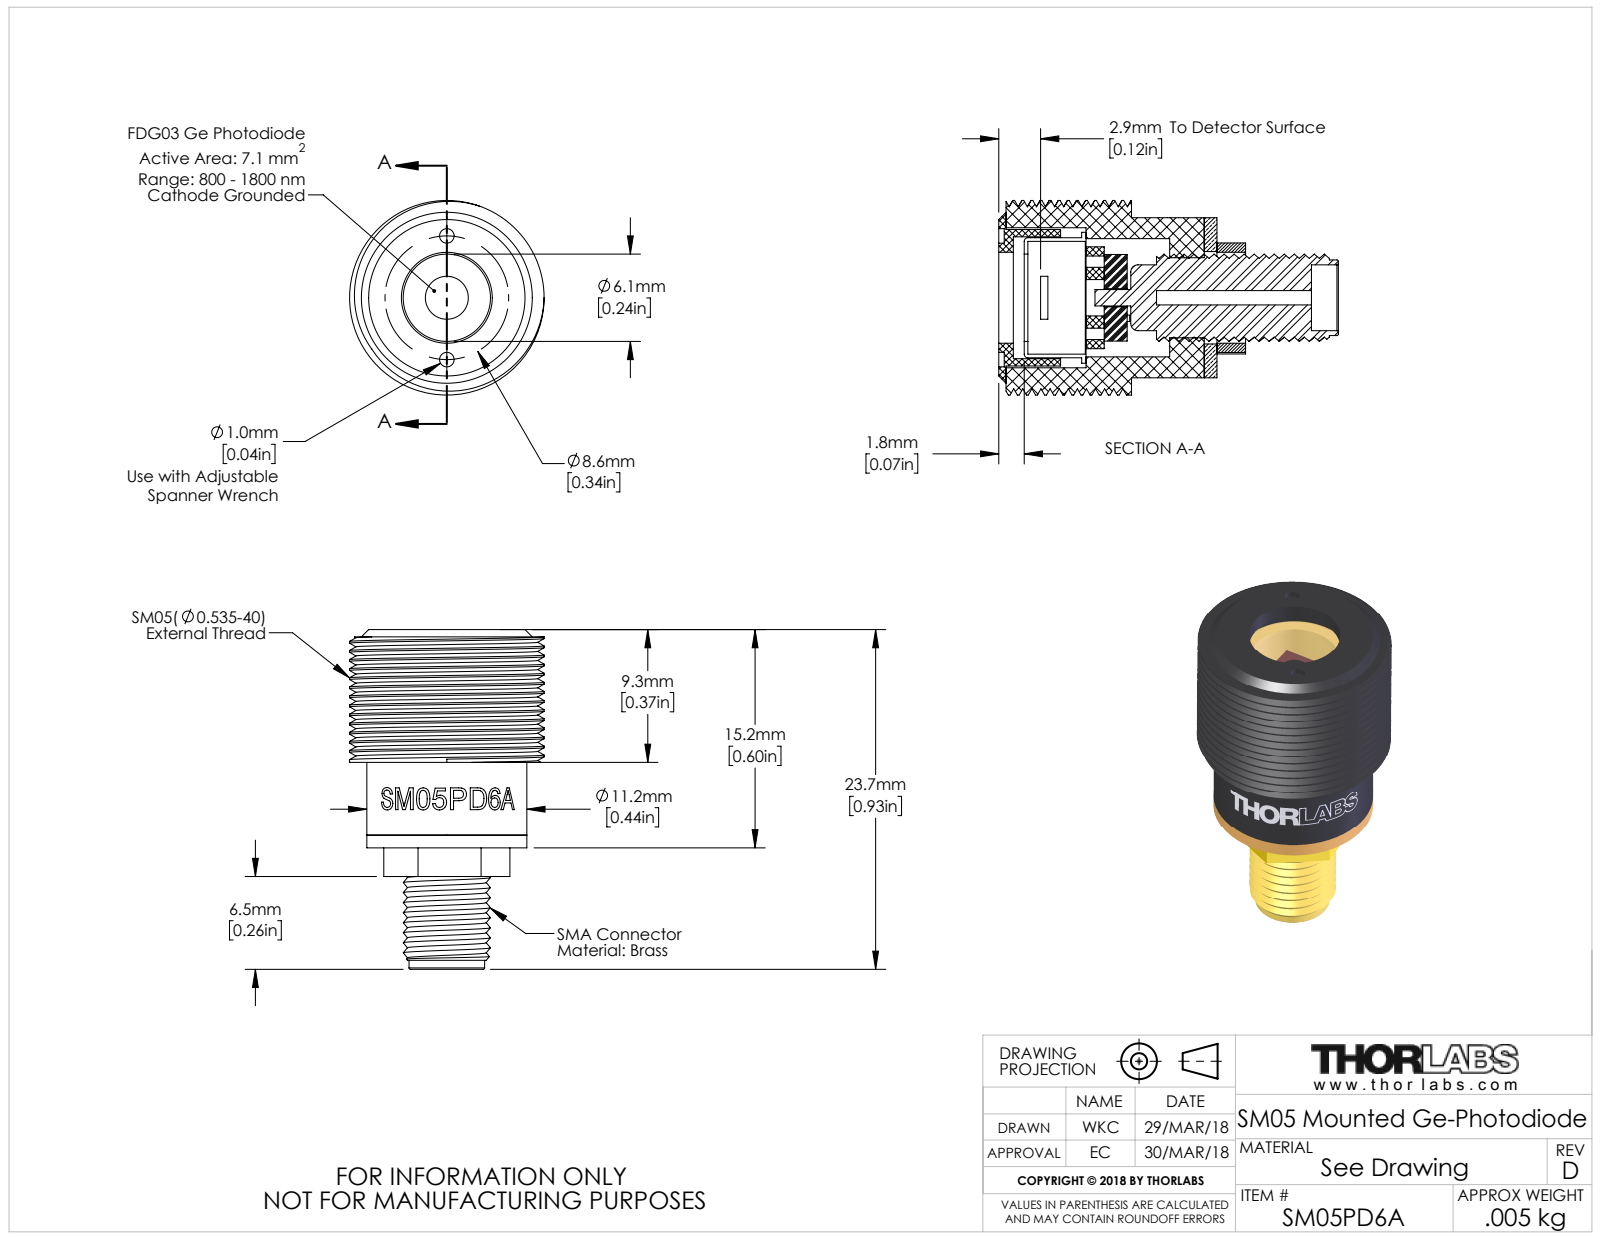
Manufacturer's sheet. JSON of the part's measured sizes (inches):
{"part_name": "13831-E0W", "step_written_by": "SolidWorks 2016 (AUTOMOTIVE_DESIGN)", "units": "inches", "bodies": {"solids": 7, "faces": 102, "planar": 37, "cylindrical": 51, "other": 14}, "overall_size": [0.924, 0.535, 0.535], "volume_in3": 0.087, "surface_area_in2": 4.49, "round_holes": [[0.04, 2], [0.039, 1], [0.181, 1], [0.22, 1], [0.24, 1], [0.25, 1], [0.254, 1], [0.31, 1], [0.325, 1], [0.335, 1], [0.385, 1]], "round_bosses_or_shafts": [[0.018, 2], [0.535, 1], [0.44, 1], [0.375, 1], [0.36, 1], [0.33, 1], [0.208, 1], [0.118, 1]], "face_to_face_distances": [0.02, 0.035, 0.335, 0.37, 0.58, 0.545, 0.21, 0.6, 0.565, 0.23], "hole_center_spacings": [0.17, 0.34]}
